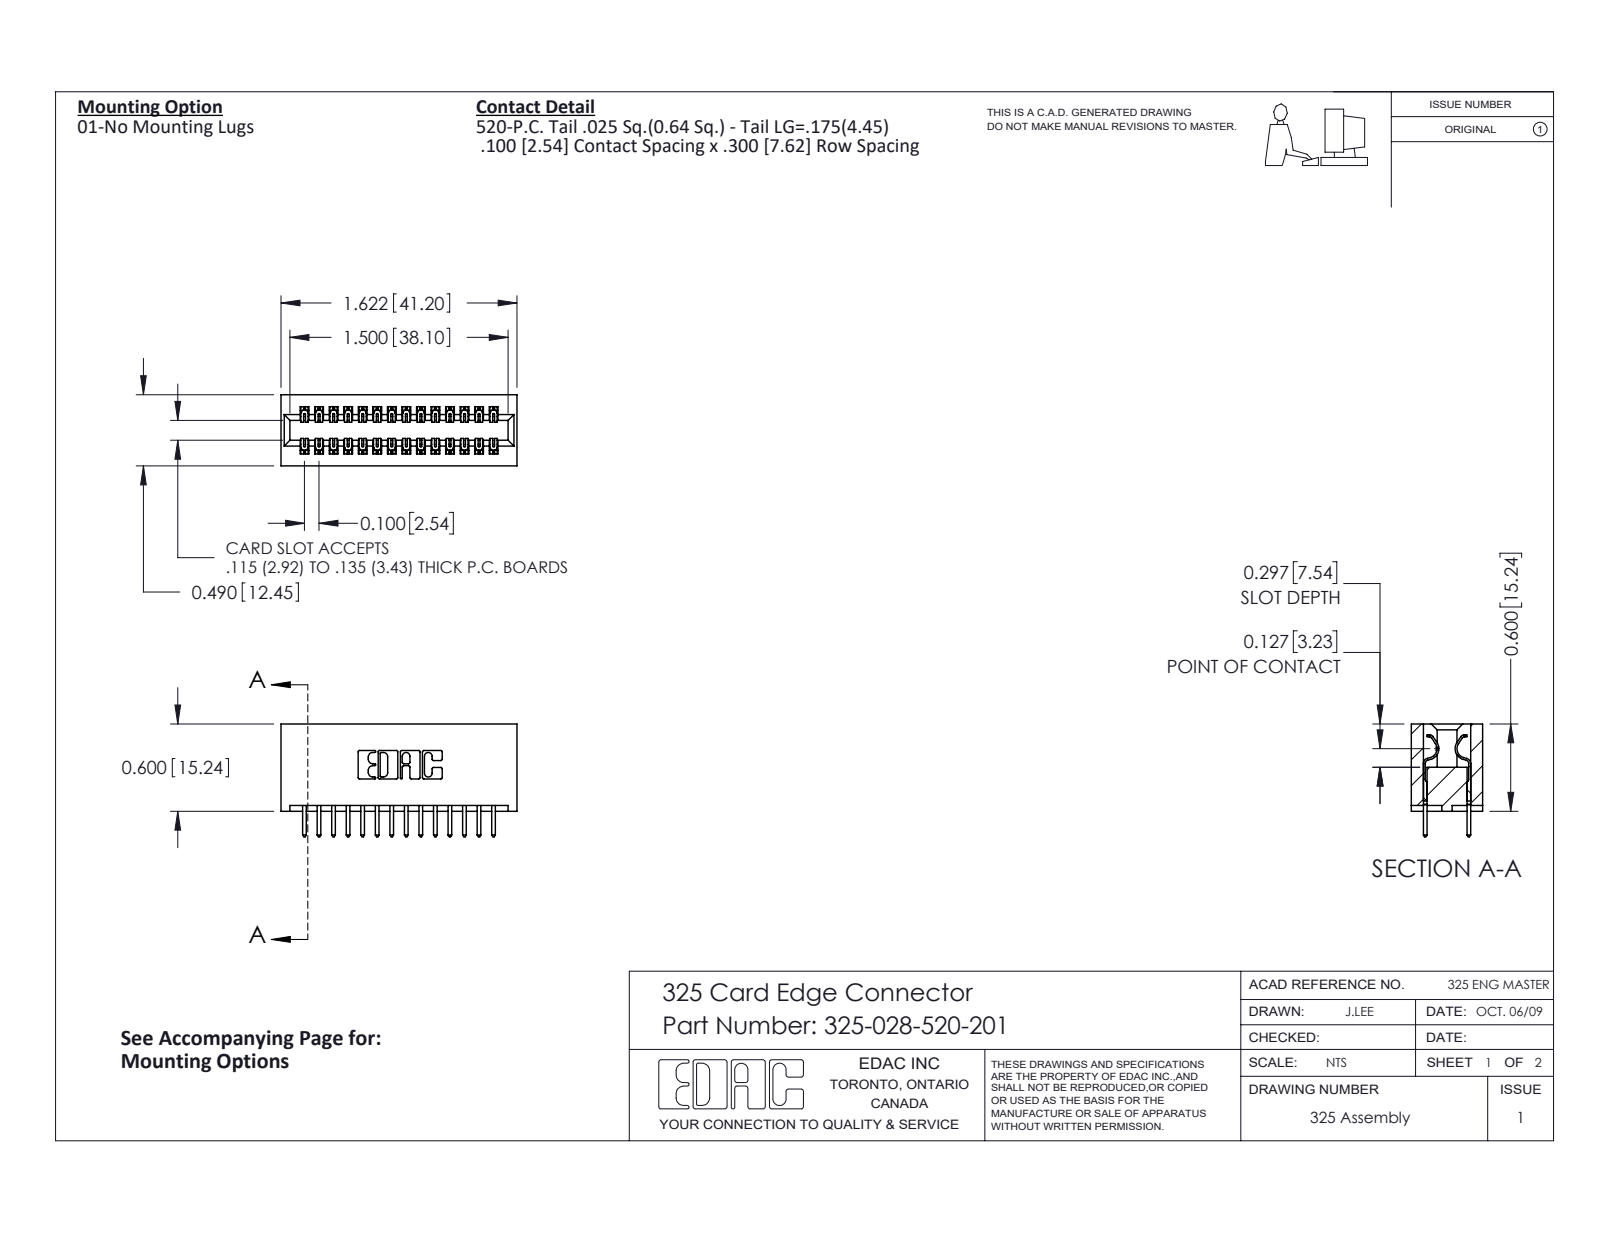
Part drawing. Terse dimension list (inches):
name: 325-292-001_325-293-120; 325 Part_Lugless; 325-028-520-201
written by: SolidWorks 2016 (CONFIG_CONTROL_DESIGN)
unit: in
bodies: 29 solids, 1562 faces (1074 planar, 488 cylindrical, 0 other)
size: 1.622 × 0.775 × 0.49
volume: 0.346 in³; area: 10.54 in²
rounds: 42× R0.006, 28× R0.01, 22× R0.01, 6× R0.007, 6× R0.031, 3× R0.026, 2× R0.014, 2× R0.022
face distances: 0.083, 0.407, 0.3, 0.49, 0.1, 0.107, 0.383, 0.025, 0.2, 0.325
